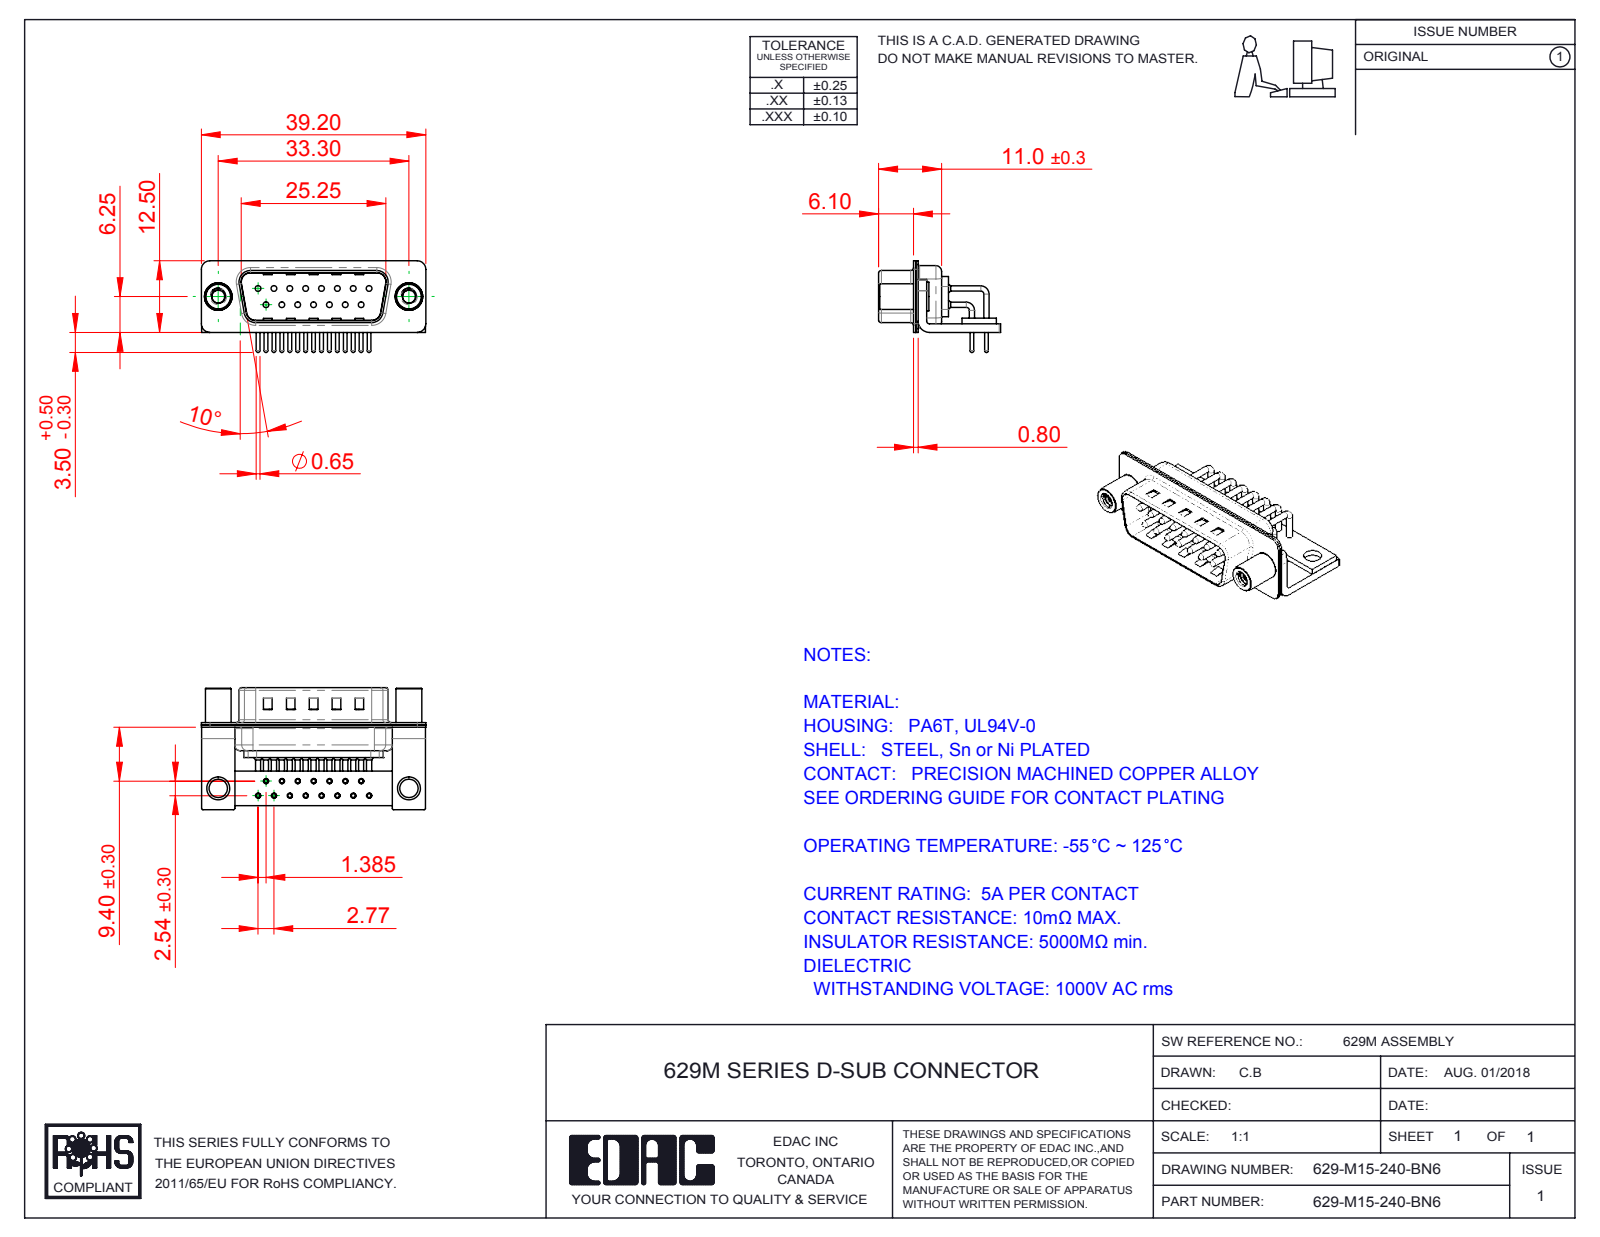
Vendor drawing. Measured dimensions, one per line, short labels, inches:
name: 629M Shell Front_15 Contacts; 629M Stabilizer Board_15 Contacts; 629M Stabilizer Bracket; 629-M15-240-BN6 (+5 more)
written by: SolidWorks 2016 (CONFIG_CONTROL_DESIGN)
unit: in
bodies: 23 solids, 2120 faces (1127 planar, 767 cylindrical, 226 other)
size: 1.543 × 0.839 × 0.63
volume: 0.156 in³; area: 10.61 in²
holes: 15× ⌀0.035, 15× ⌀0.039, 15× ⌀0.067, 15× ⌀0.079, 2× ⌀0.089, 2× ⌀0.126, 2× ⌀0.157, 2× ⌀0.189
bosses: 21× ⌀0.035, 15× ⌀0.059, 15× ⌀0.026, 2× ⌀0.197, 2× ⌀0.193, 2× ⌀0.177
rounds: 16× R0.01, 16× R0.059, 15× R0.04, 13× R0.079, 9× R0.02, 8× R0.063, 4× R0.024, 4× R0.026
face distances: 0.016, 0.059, 0.033, 0.031, 0.049, 0.409, 0.376, 0.075, 0.039, 0.327
hole spacings: 0.109, 0.218, 0.124, 0.327, 0.192, 0.436, 0.114, 0.29
